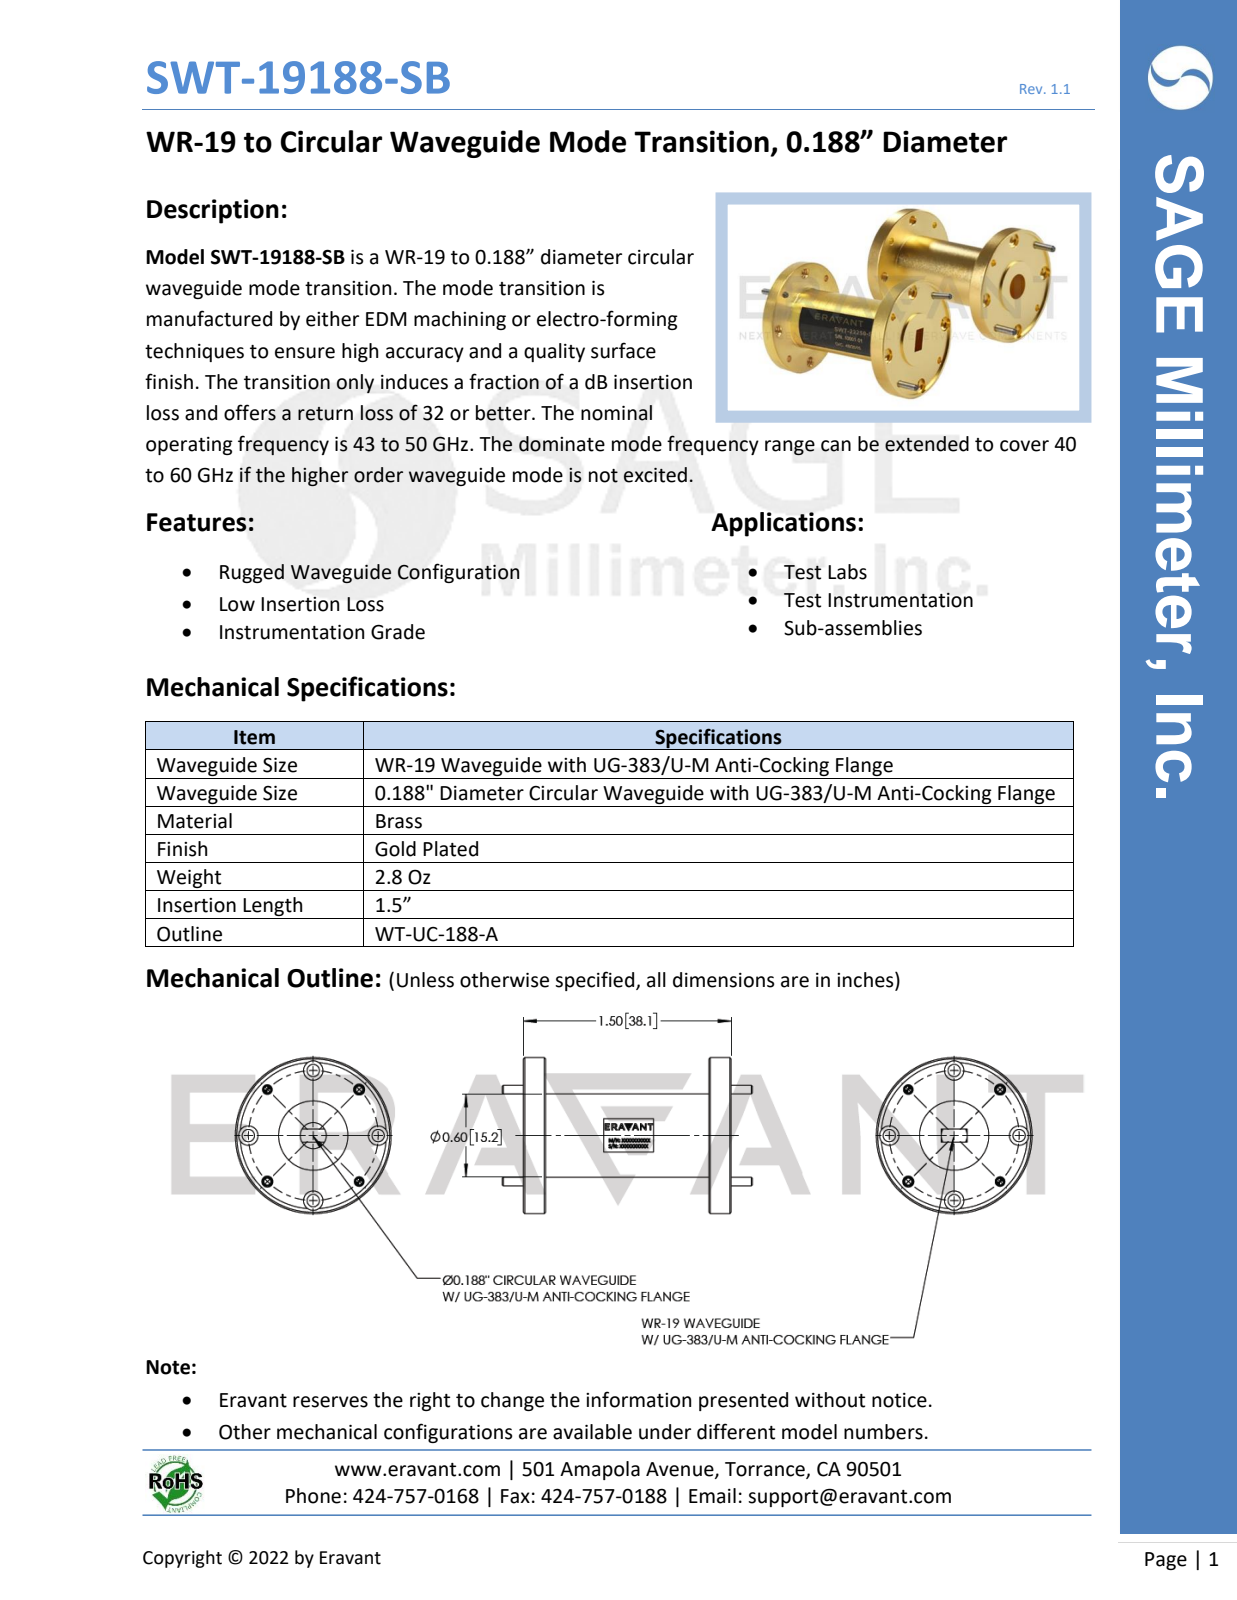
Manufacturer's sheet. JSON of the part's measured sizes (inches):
{"part_name": "WT-UC-188-A", "step_written_by": "SolidWorks 2021 (AUTOMOTIVE_DESIGN)", "units": "inches", "bodies": {"solids": 5, "faces": 148, "planar": 26, "cylindrical": 74, "other": 48}, "overall_size": [1.805, 1.125, 1.125], "volume_in3": 0.614, "surface_area_in2": 7.588, "round_holes": [[0.061, 4], [0.067, 4], [0.089, 4], [0.14, 4], [1.055, 1], [1.055, 1]], "round_bosses_or_shafts": [[0.063, 4], [1.125, 1], [0.6, 1], [0.5, 1]], "face_to_face_distances": [0.14, 1.32, 1.18, 1.46, 1.48, 1.34, 0.16, 0.02, 0.02, 0.16], "hole_center_spacings": [0.359, 0.663, 0.866, 0.469, 0.938, 0.469, 0.937]}
